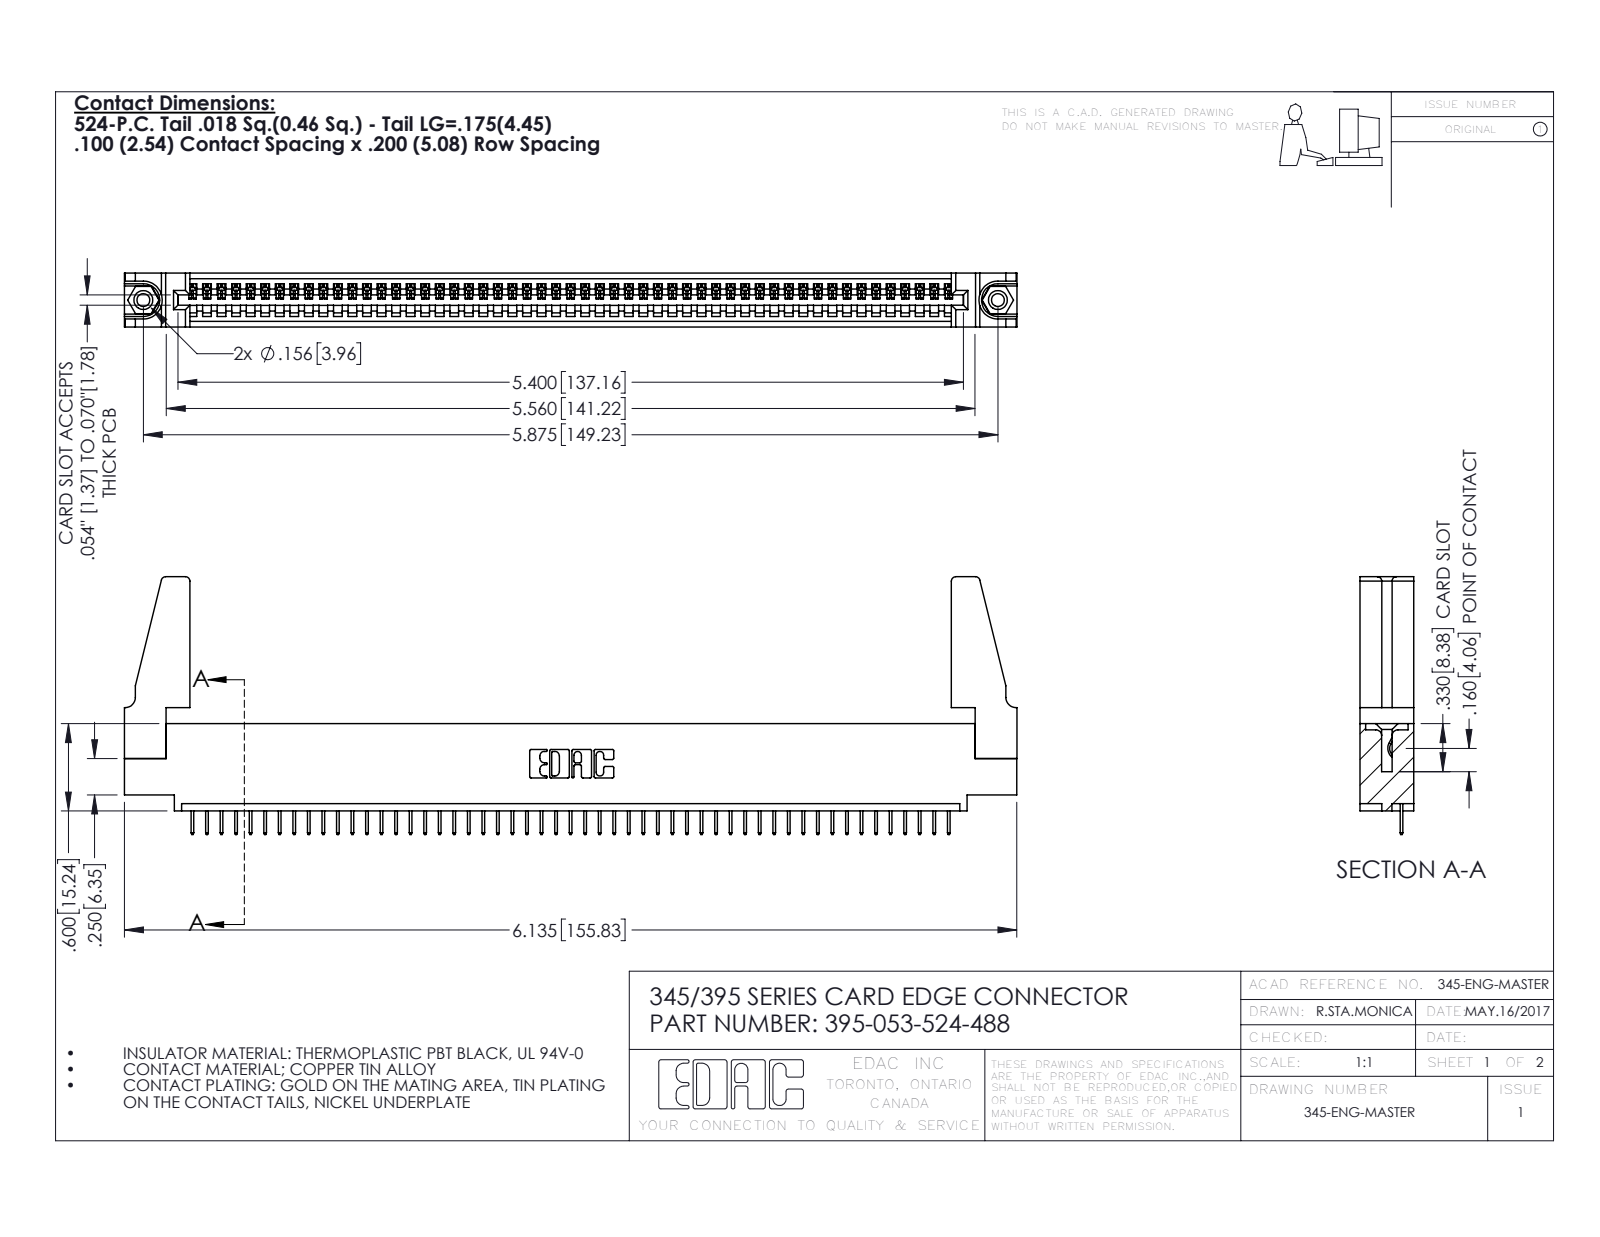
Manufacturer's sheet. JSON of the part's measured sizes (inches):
{"part_name": "345-292-001_345-293-124; 395-053-524-488; 345-220-078_345-220-088; 345-250-001_345-250-001-102 (+1 more)", "step_written_by": "SolidWorks 2016 (CONFIG_CONTROL_DESIGN)", "units": "inches", "bodies": {"solids": 58, "faces": 3540, "planar": 2594, "cylindrical": 930, "other": 16}, "overall_size": [6.136, 1.772, 0.37], "volume_in3": 1.09, "surface_area_in2": 34.27, "round_holes": [[0.089, 2], [0.125, 2], [0.156, 2], [0.064, 1]], "round_bosses_or_shafts": [[0.155, 2]], "partial_cylinders_radius": [[0.006, 106], [0.01, 22], [0.03, 8], [0.007, 6], [0.031, 6], [0.026, 3], [0.031, 2], [0.04, 2]], "face_to_face_distances": [0.072, 0.298, 0.37, 0.2, 0.098, 0.272, 0.025, 0.225, 0.072, 0.149], "hole_center_spacings": [0.27, 5.639, 5.875]}
